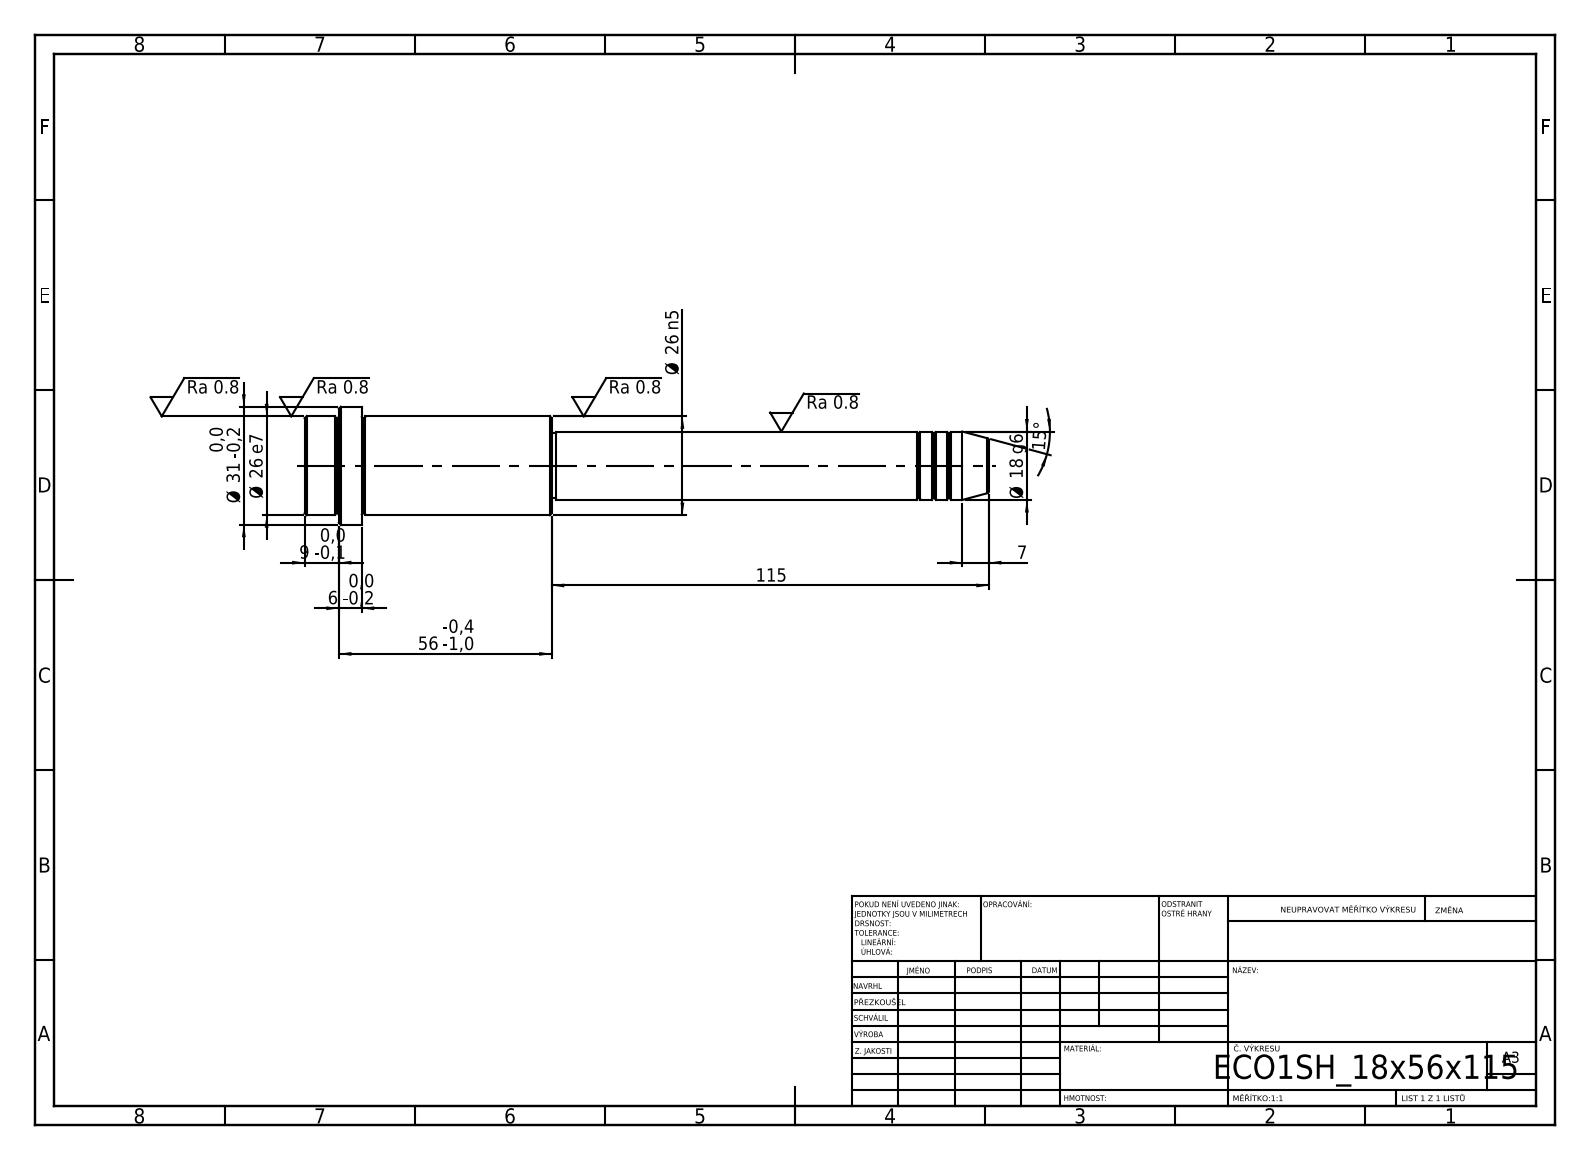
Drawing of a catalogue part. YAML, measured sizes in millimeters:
step_written_by: "SolidWorks 2019 (CONFIG_CONTROL_DESIGN)"
units: millimeters
bodies: {solids: 1, faces: 52, planar: 6, cylindrical: 16, other: 30}
overall_size: [180, 31, 31]
volume: 64583
surface_area: 13436
round_bosses_or_shafts:
  - {diameter: 31, count: 1}
  - {diameter: 26, count: 1}
  - {diameter: 18, count: 1}
  - {diameter: 17, count: 1}
face_to_face_distances: [65, 50, 15, 56, 6, 9, 115, 165, 171, 180]
